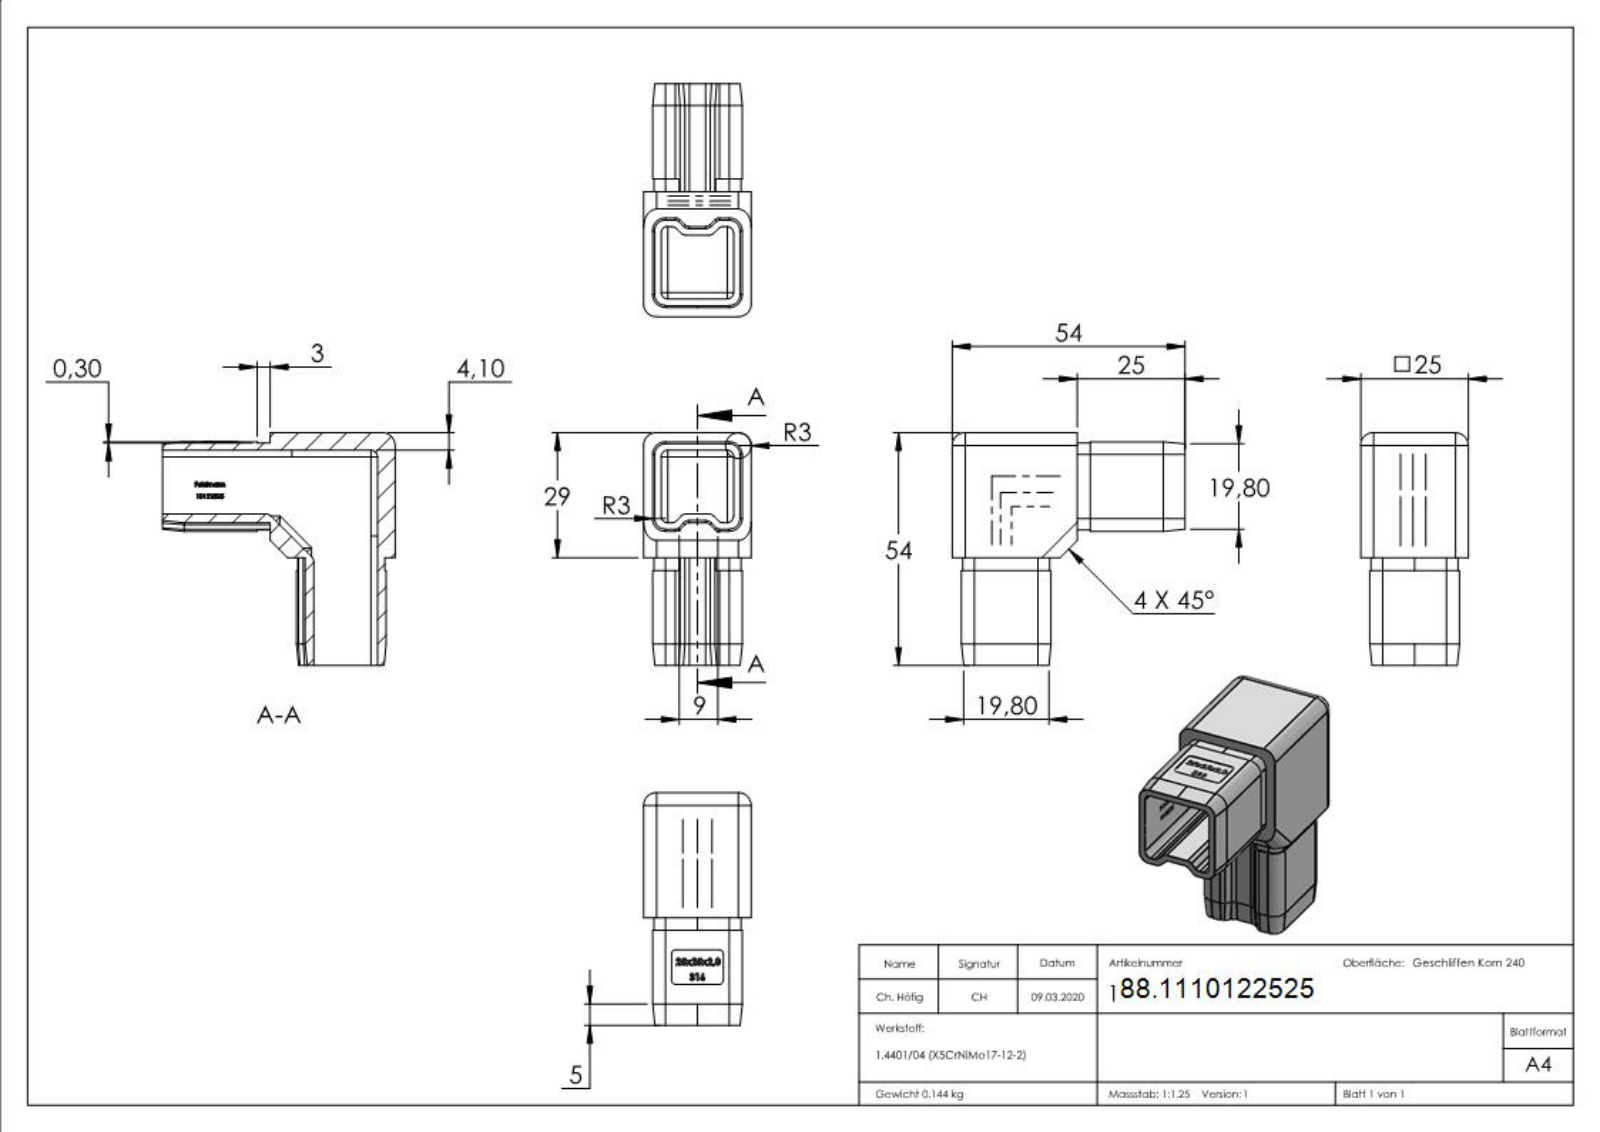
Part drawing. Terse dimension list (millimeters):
name: 10122525
written by: SolidWorks 2015 (CONFIG_CONTROL_DESIGN)
unit: mm
bodies: 1 solid, 556 faces (300 planar, 68 cylindrical, 188 other)
size: 54 × 54 × 25
volume: 18 035 mm³; area: 13 156 mm²
rounds: 35× R1.5, 15× R3, 8× R2.7, 4× R1
face distances: 4.1, 2, 16.8, 20.9, 2.1, 18.8, 22.9, 25, 20.8, 24.9
